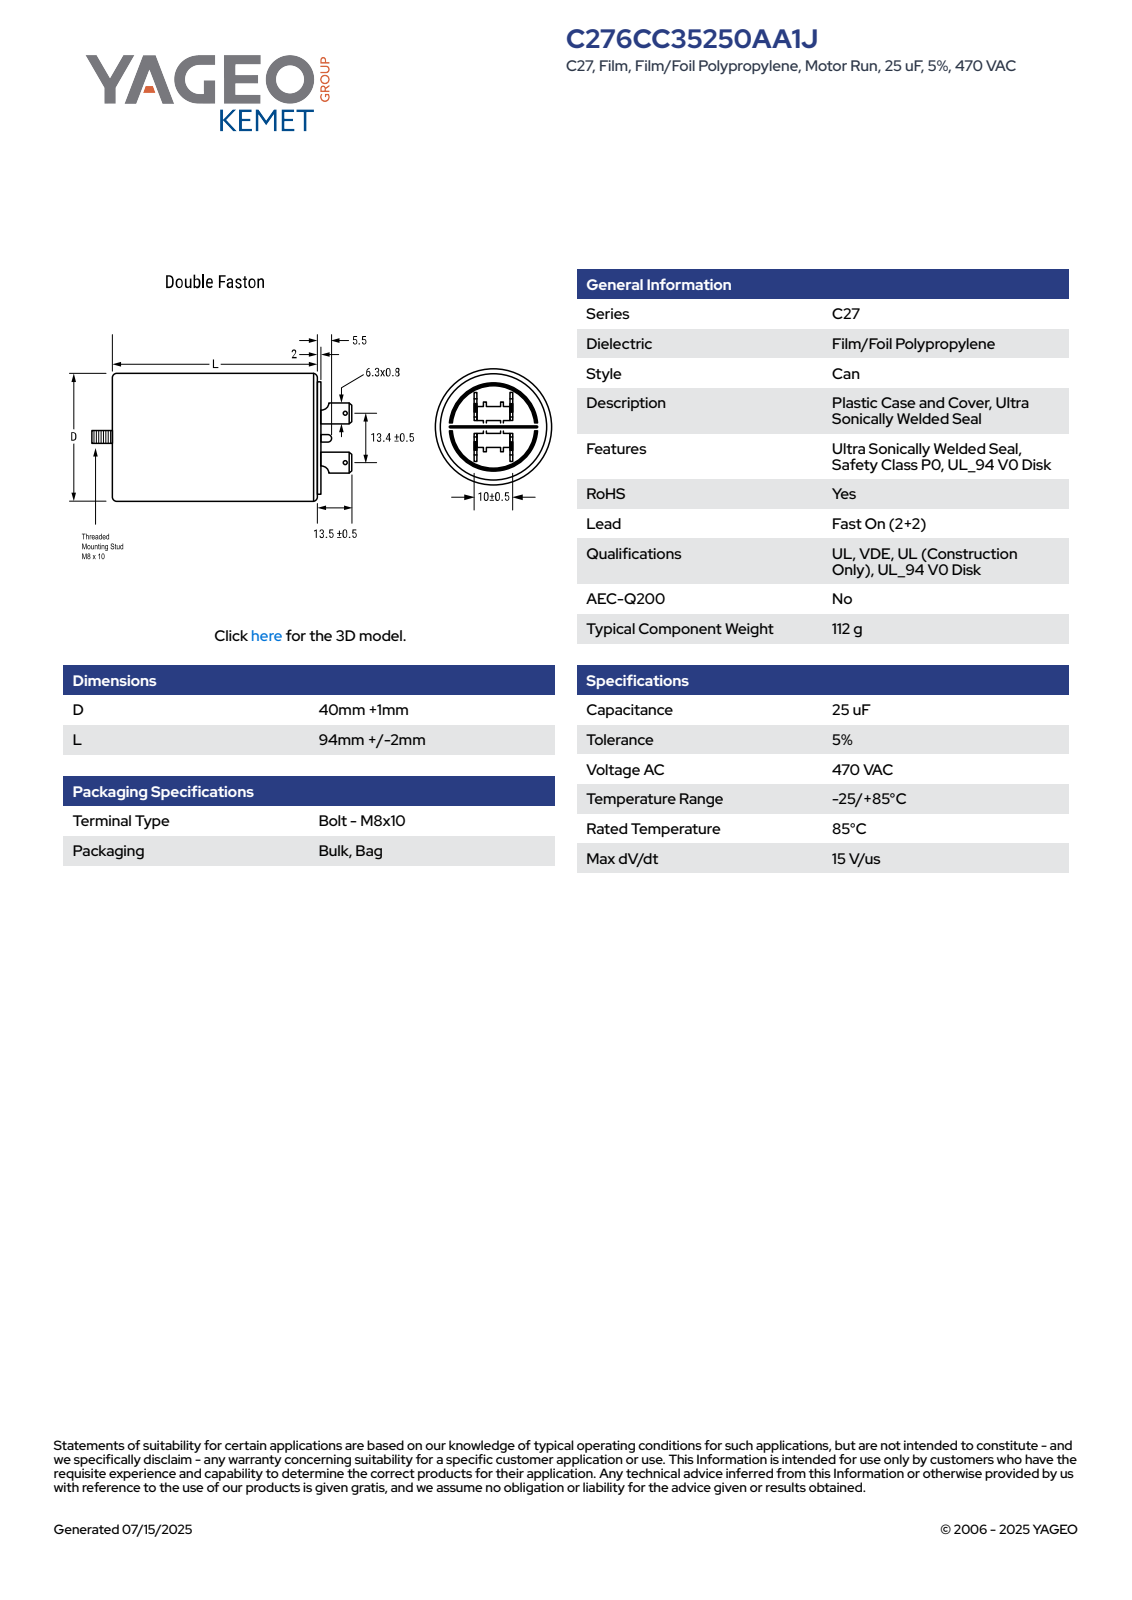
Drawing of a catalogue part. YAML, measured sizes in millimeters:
part_name: "CFM_C27DF_40X94_D41L96"
step_written_by: "SolidWorks 2014 (AUTOMOTIVE_DESIGN)"
units: millimeters
bodies: {solids: 1, faces: 137, planar: 49, cylindrical: 53, other: 35}
overall_size: [120, 41, 41]
volume: 128871
surface_area: 16105
round_holes:
  - {diameter: 1.2, count: 2}
round_bosses_or_shafts:
  - {diameter: 41, count: 1}
  - {diameter: 31.54, count: 1}
  - {diameter: 8, count: 1}
partial_cylinders:
  - {radius: 0.25, count: 9}
  - {radius: 4, count: 2}
  - {radius: 20.49, count: 1}
face_to_face_distances: [98, 96, 2, 0.8, 9.7, 8.9, 10.5, 0.5, 10, 106]
hole_center_spacings: [13.9]
